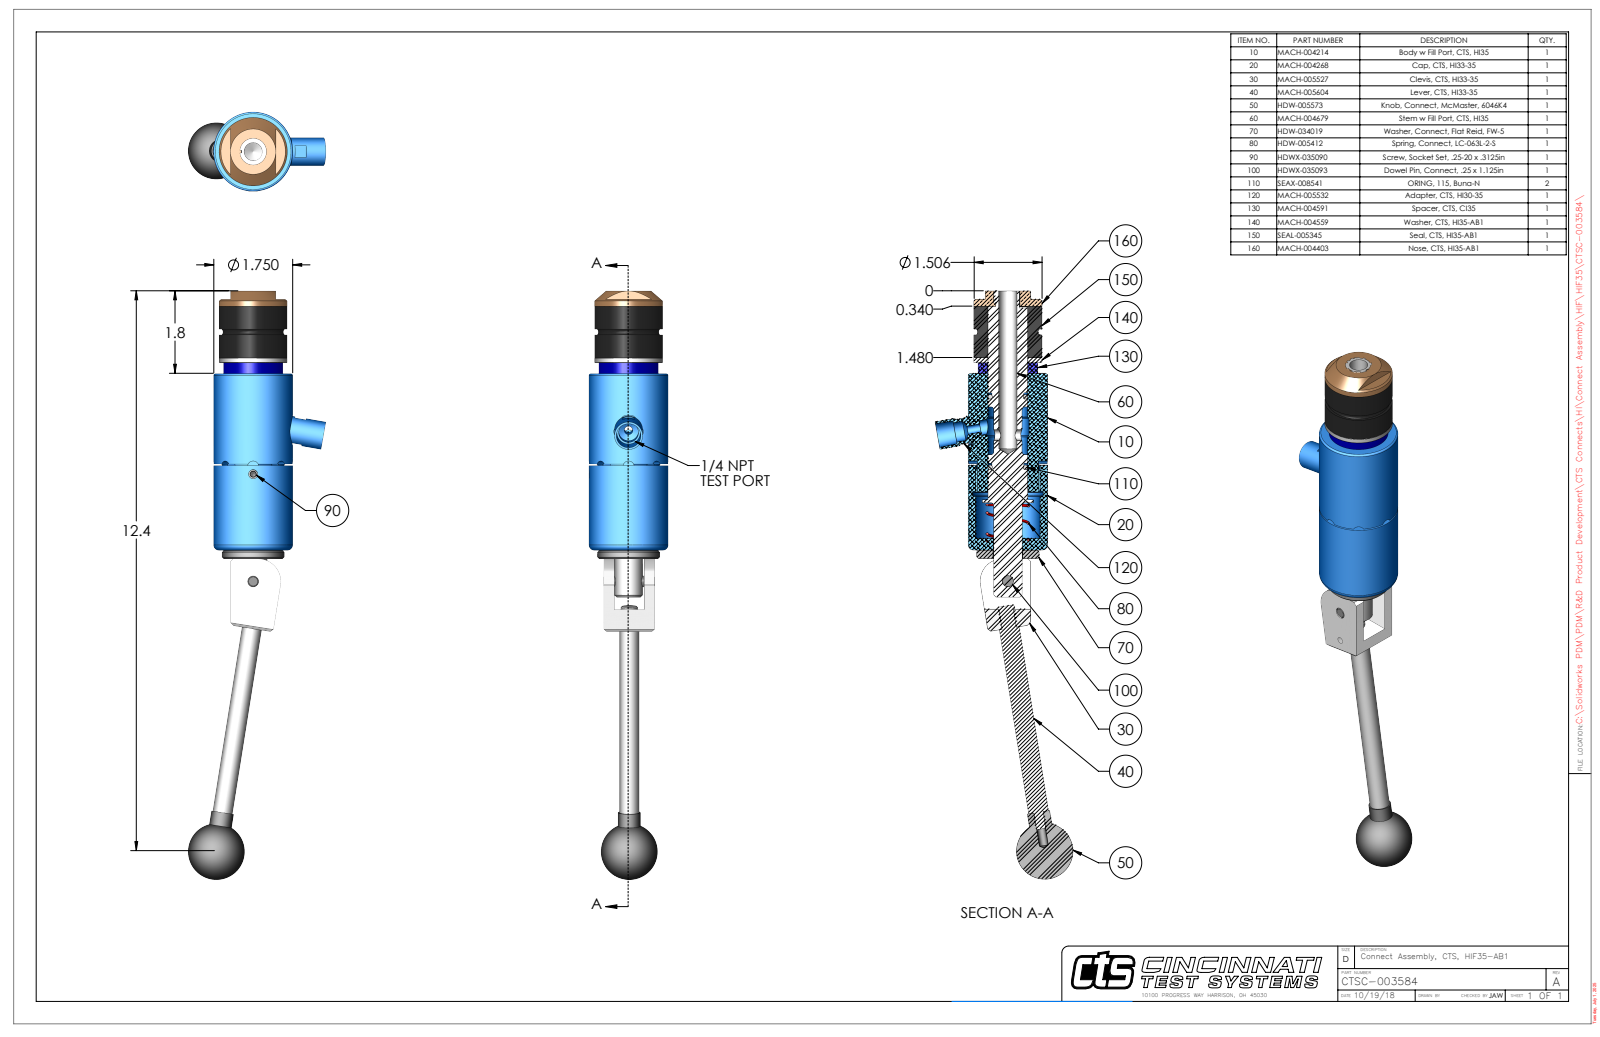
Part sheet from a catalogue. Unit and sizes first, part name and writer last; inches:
Units: inches
Overall size (bounding box): 13.042 × 3.043 × 1.75
Round holes (diameter × count): ⌀0.201 ×2, ⌀0.15 ×1, ⌀0.187 ×1, ⌀0.249 ×1, ⌀0.25 ×1, ⌀0.251 ×1, ⌀0.313 ×1, ⌀0.406 ×1, ⌀0.438 ×1, ⌀0.531 ×1, ⌀0.635 ×1, ⌀0.656 ×1
Round bosses / shafts (diameter × count): ⌀0.25 ×2, ⌀1.75 ×1, ⌀1.506 ×1, ⌀1.38 ×1, ⌀1.312 ×1, ⌀0.869 ×1, ⌀0.625 ×1, ⌀0.62 ×1
Partial cylindrical surfaces — rounded edges, fillets, slot ends (radius × count): R0.125 ×4, R0.029 ×2, R0.248 ×1, R0.33 ×1, R0.5 ×1, R0.695 ×1, R0.835 ×1
Main face-to-face distances: 5.405, 1.49, 3.915, 1.14, 0.35, 4.265, 1.25, 0.11, 0.24, 4.155
Hole centre spacings: 0.74, 2.376, 3.116
Volume: 15.18 in³ · Surface area: 92.8 in²
Bodies: 10 solids, 291 faces (106 planar, 120 cylindrical, 65 other)
Part name (STEP PRODUCT): CTSC-003584
STEP written by: SolidWorks 2023 (AUTOMOTIVE_DESIGN)
